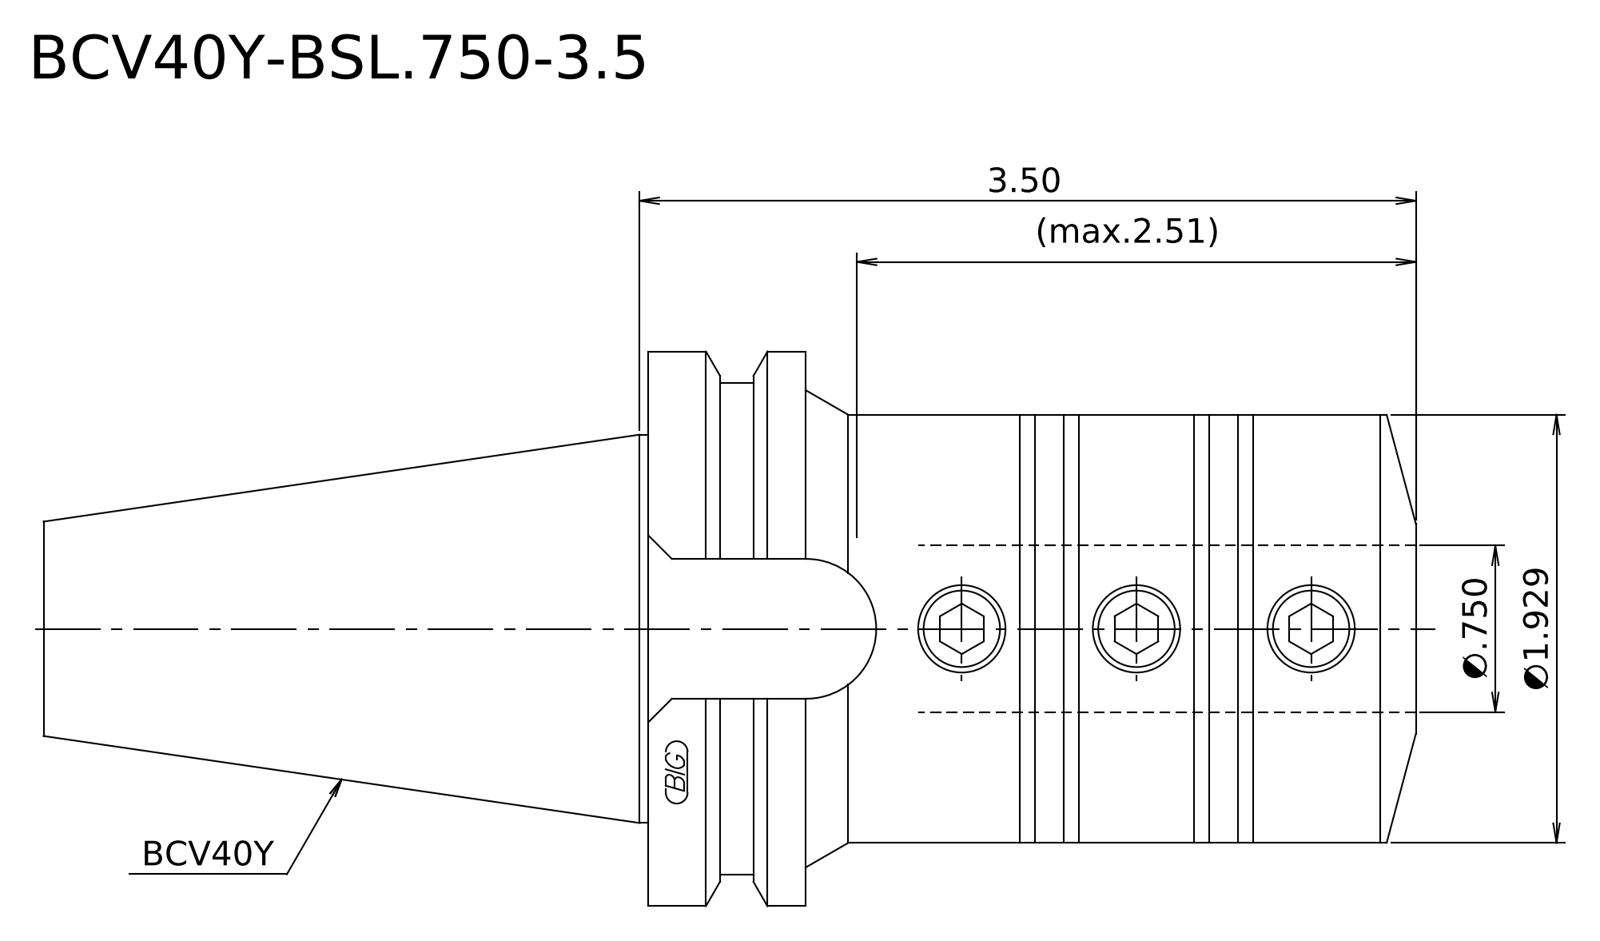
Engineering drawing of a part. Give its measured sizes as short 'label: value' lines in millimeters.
written by: Kubotek KeyCreator 2011 V10.0.2 (22737) (automotive_design)
unit: mm
bodies: 1 solid, 16 faces (6 planar, 5 cylindrical, 5 other)
size: 157.15 × 63.5 × 63.5
volume: 250 958 mm³; area: 27 249 mm²
bosses: 1× ⌀63.5, 1× ⌀56.36, 1× ⌀49, 1× ⌀44.45
face distances: 18.05, 87.3, 69.25, 69.85, 87.9, 157.15, 79.7, 9.85, 8.2, 77.45
